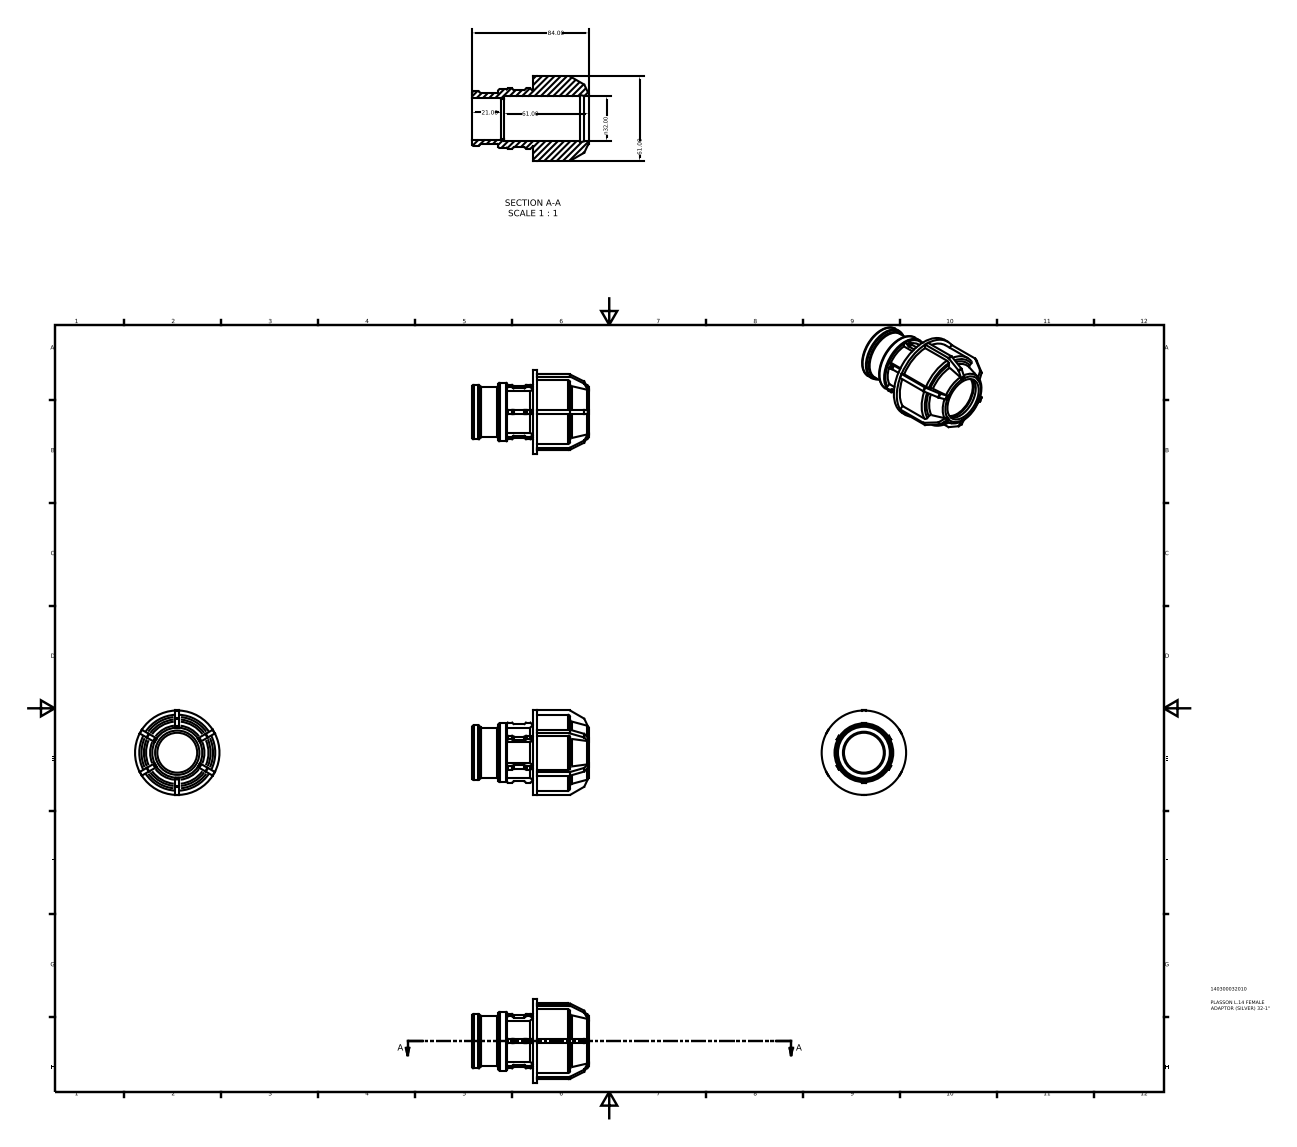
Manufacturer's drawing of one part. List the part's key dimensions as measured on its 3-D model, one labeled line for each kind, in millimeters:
Part name (STEP PRODUCT): 140300032010
STEP written by: Autodesk Inventor 2015 (AUTOMOTIVE_DESIGN)
Units: millimetres
Bodies: 1 solid, 261 faces (160 planar, 68 cylindrical, 33 other)
Overall size (bounding box): 84 × 61 × 61
Volume: 70 898 mm³ · Surface area: 27 027 mm²
Round holes (diameter × count): ⌀28.8 ×1, ⌀30.29 ×1, ⌀32 ×1
Round bosses / shafts (diameter × count): ⌀61 ×1, ⌀54.9 ×1, ⌀42.41 ×1, ⌀39.38 ×1, ⌀36.35 ×1
Partial cylindrical surfaces — rounded edges, fillets, slot ends (radius × count): R0.96 ×48
Main face-to-face distances: 3.05, 3.04, 3.06, 43.74, 46.79, 61, 37.21, 25.15, 18.59, 21.64
